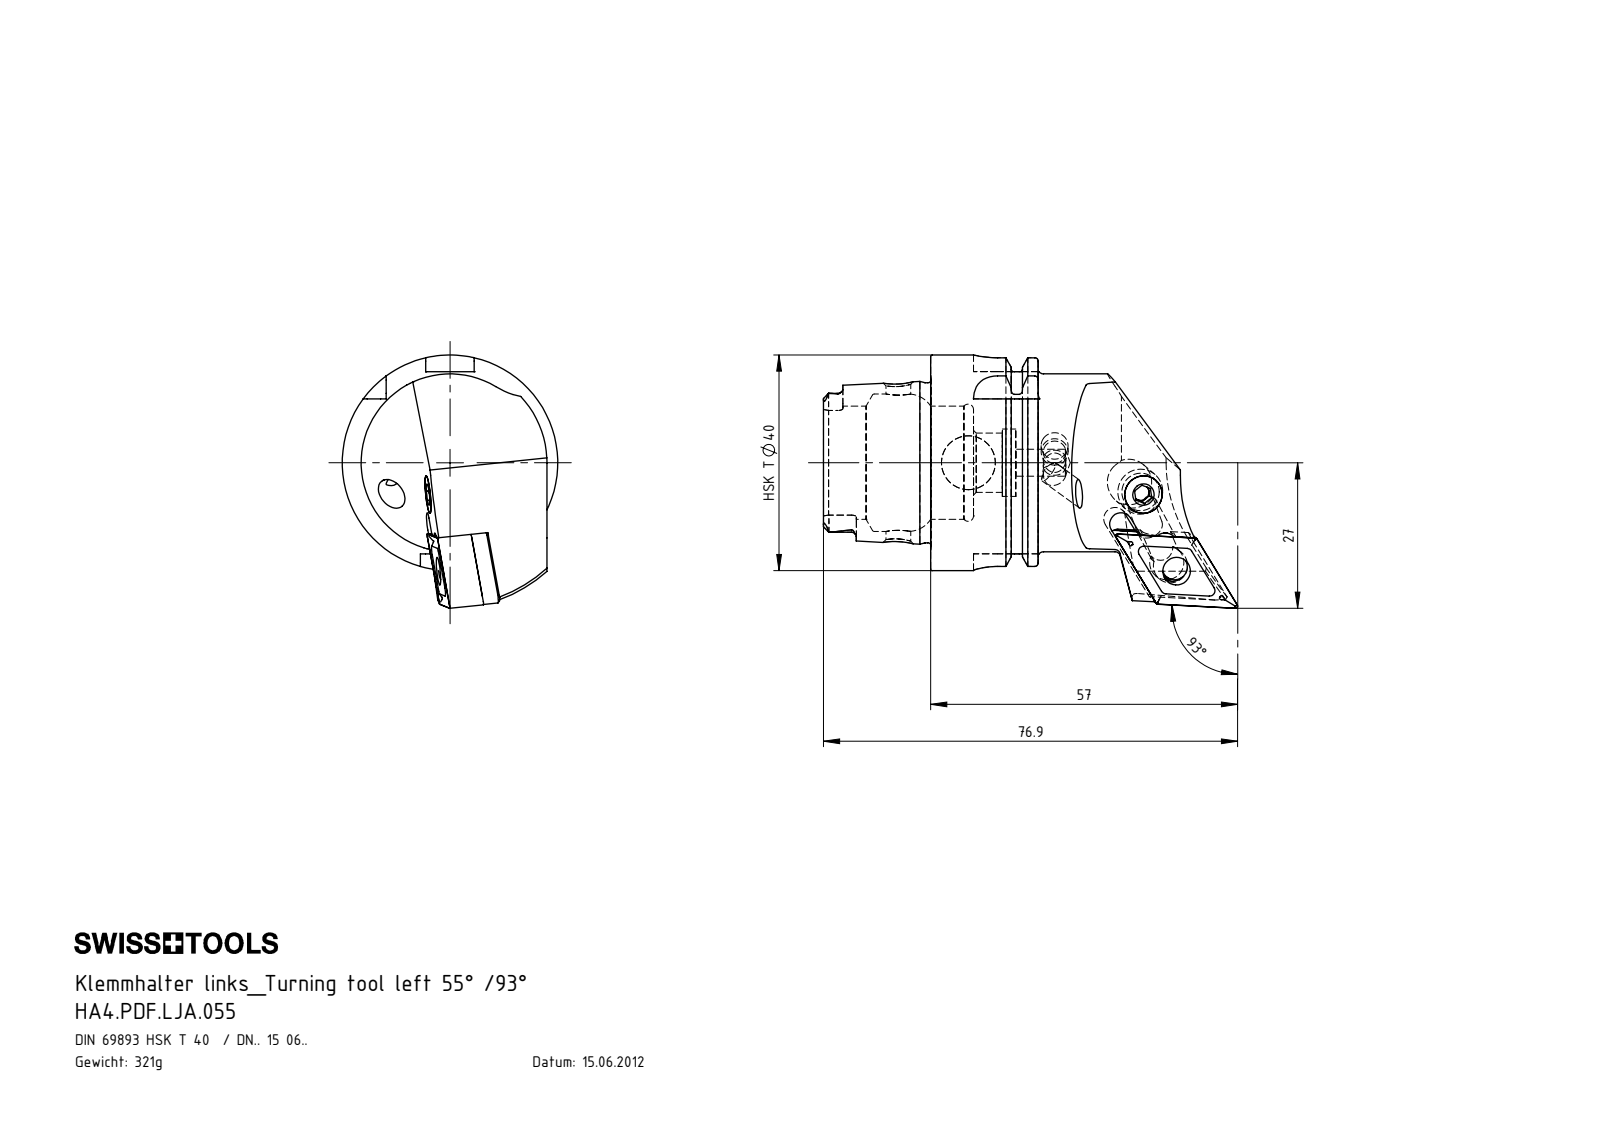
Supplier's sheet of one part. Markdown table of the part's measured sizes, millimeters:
| quantity | value |
| --- | --- |
| part name | HA4-PDF.LJA.055; KVT_MB_600_050; WCD-ER1.101.000; DNMG150604 (+4 more) |
| STEP written by | SolidWorks 2012 (CONFIG_CONTROL_DESIGN) |
| units | millimeters |
| bodies | 8 solids, 385 faces (119 planar, 106 cylindrical, 160 other) |
| overall size | 76.9 × 47 × 40 |
| volume | 42 023 mm³ |
| surface area | 16 688 mm² |
| round holes (diameter × count) | 4.2 × 2, 5 × 2, 4 × 1, 4.6 × 1, 5.16 × 1, 6.4 × 1, 7 × 1, 8.4 × 1, 10 × 1, 11 × 1, 12.5 × 1, 21 × 1 |
| round bosses / shafts (diameter × count) | 40 × 1, 34.75 × 1, 33 × 1, 29.71 × 1, 8 × 1, 7.9 × 1, 6.4 × 1, 5 × 1 |
| partial cylindrical surfaces (radius × count) | 0.9 × 6, 0.4 × 4, 1 × 4, 1.88 × 4, 4.5 × 4, 2.5 × 2, 2.1 × 1, 2.35 × 1 |
| main face-to-face distances | 6.02, 9.2, 3.18, 7.95, 19.95, 12, 12.33, 4.84, 19.9, 27.85 |
| hole center spacings | 15.59 |
